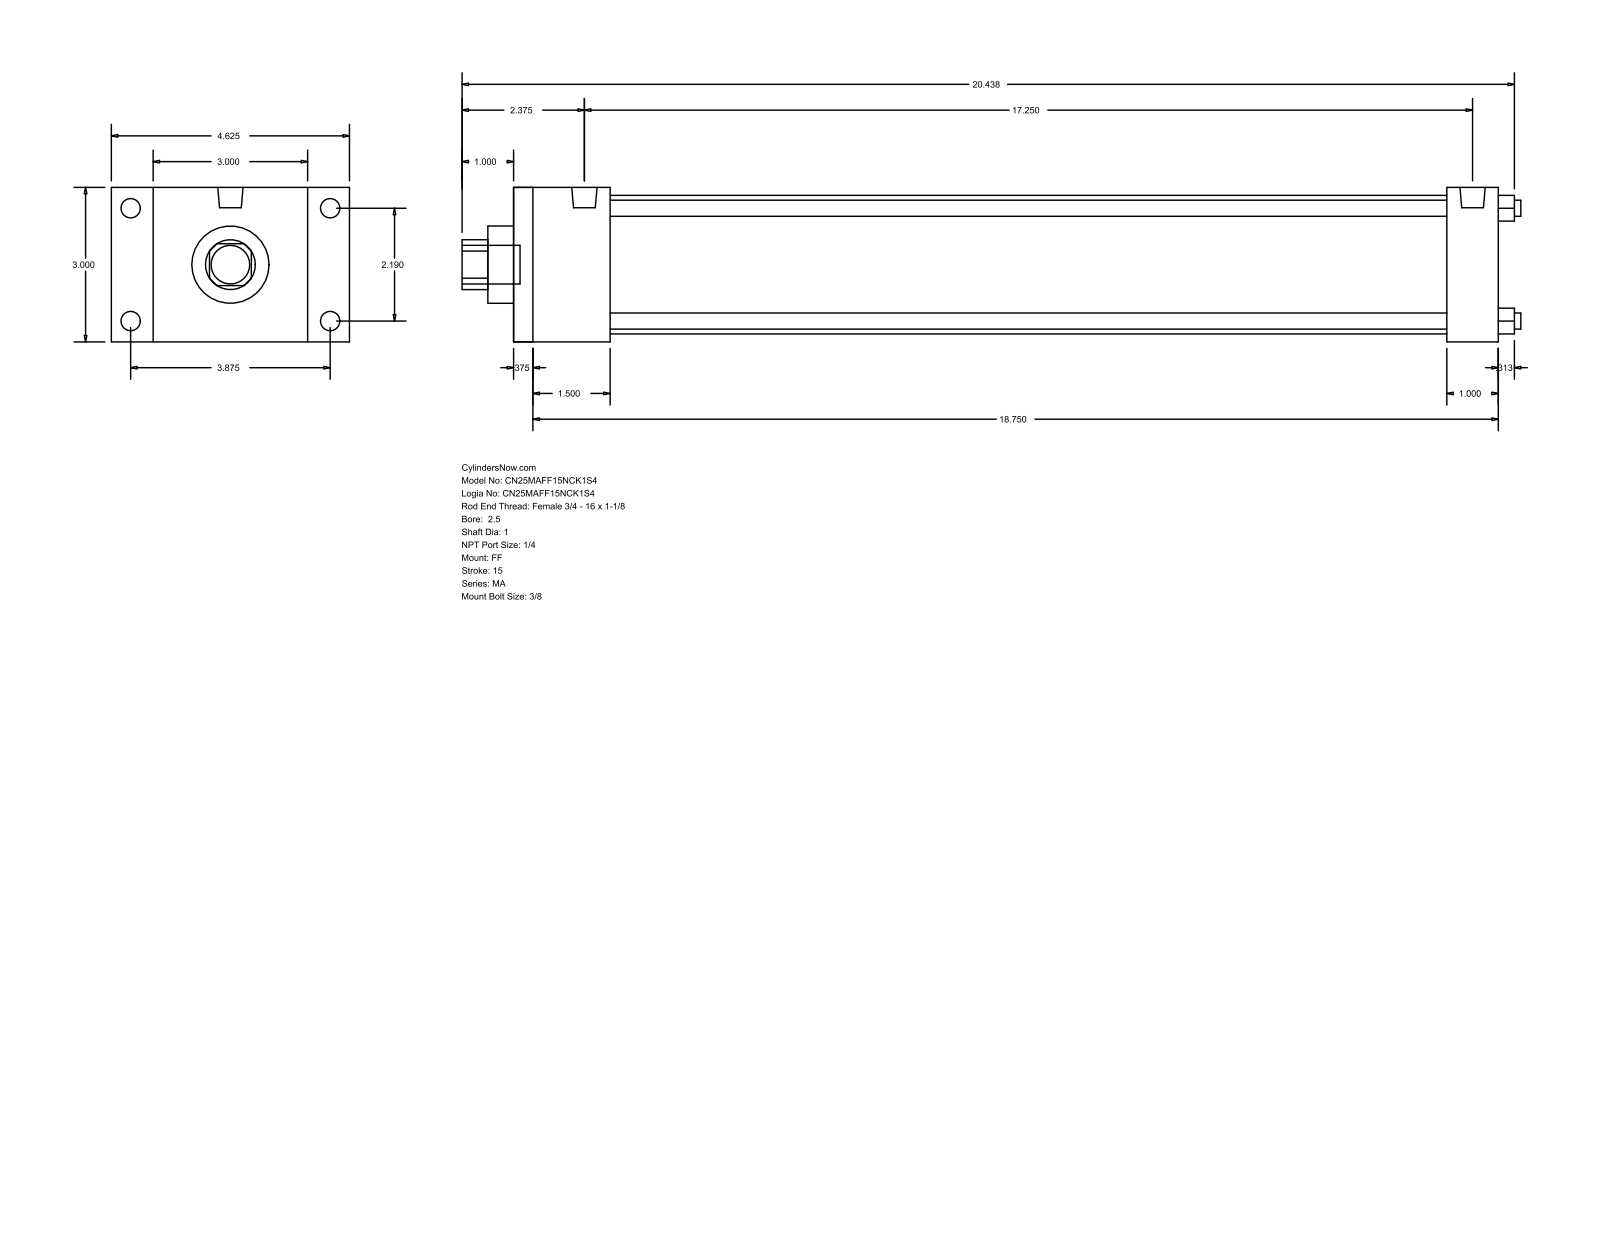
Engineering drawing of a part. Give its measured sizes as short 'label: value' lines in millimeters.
name: MA_FF__0250_1
written by: GSSL Pune (CONFIG_CONTROL_DESIGN)
unit: mm
bodies: 0 solids, 92 faces (64 planar, 28 cylindrical, 0 other)
size: 522.29 × 117.47 × 76.2
holes: 4× ⌀7.94, 1× ⌀25.4, 1× ⌀38.1, 1× ⌀68.33
bosses: 4× ⌀9.53, 4× ⌀7.94, 2× ⌀12.49, 1× ⌀19.05
rounds: 1× R12.29
face distances: 76.2, 485.78, 9.52, 476.26, 47.63, 460.37, 38.11, 450.85, 412.74, 438.15
hole spacings: 39.33, 55.62, 78.66
